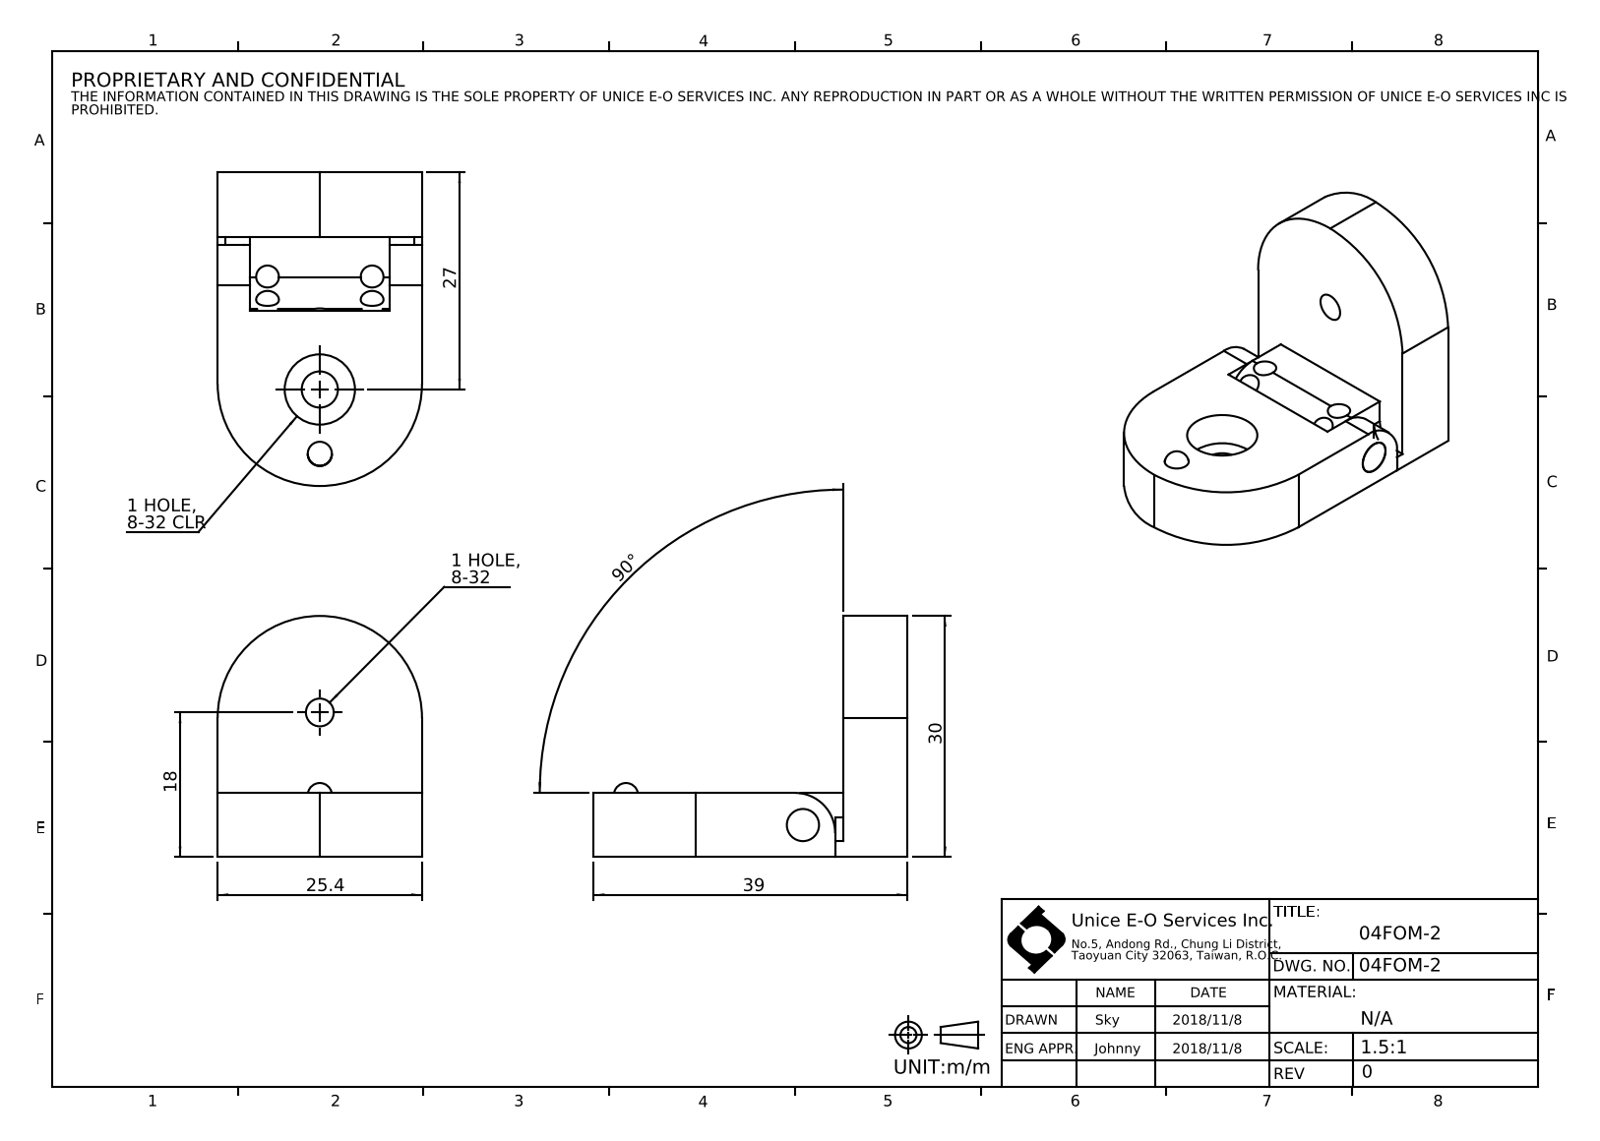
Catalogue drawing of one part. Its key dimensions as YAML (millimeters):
part_name: "04FOM-2"
step_written_by: "SolidWorks 2016 (AUTOMOTIVE_DESIGN)"
units: millimeters
bodies: {solids: 0, faces: 56, planar: 22, cylindrical: 24, other: 10}
overall_size: [39, 30, 25.4]
round_holes:
  - {diameter: 3, count: 1}
  - {diameter: 3.45, count: 1}
  - {diameter: 4, count: 1}
  - {diameter: 4.5, count: 1}
  - {diameter: 8.73, count: 1}
partial_cylinders:
  - {radius: 3, count: 2}
  - {radius: 12.7, count: 2}
  - {radius: 4, count: 1}
  - {radius: 5, count: 1}
face_to_face_distances: [8, 25.4, 4, 21.4, 17.2, 9.2, 17.4, 4.32, 3.68, 9]
hole_center_spacings: [8]
